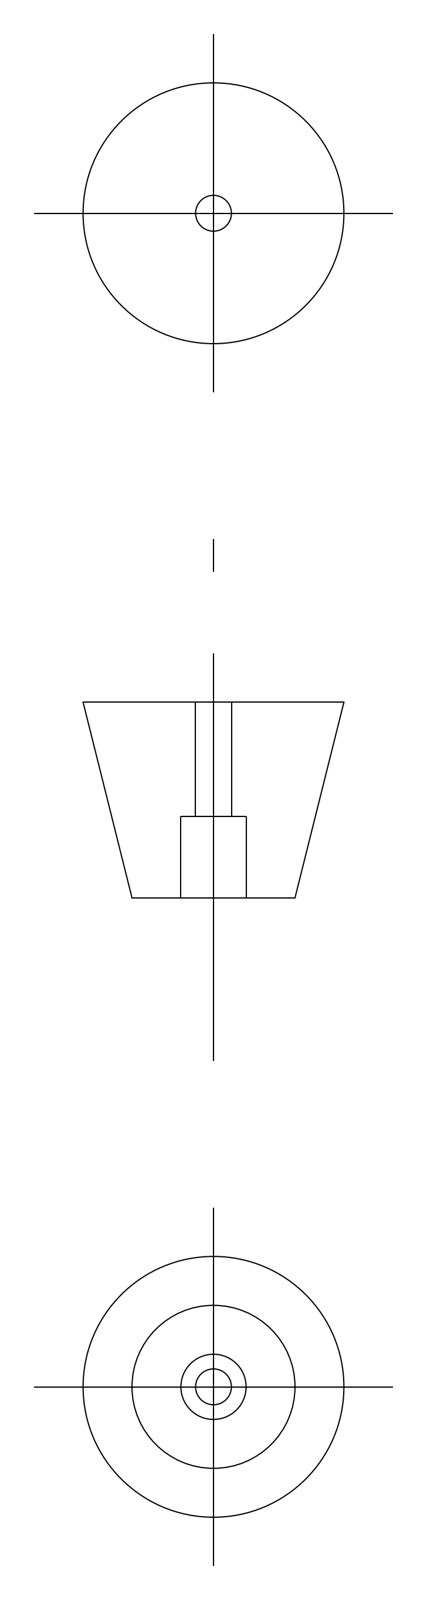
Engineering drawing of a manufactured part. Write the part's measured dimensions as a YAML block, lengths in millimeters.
part_name: "washer; rubber foot; K3W_6375_36"
step_written_by: "CADfix (AUTOMOTIVE_DESIGN)"
units: millimeters
bodies: {solids: 2, faces: 21, planar: 0, cylindrical: 0, other: 21}
overall_size: [16, 16, 12]
volume: 1535
surface_area: 947
